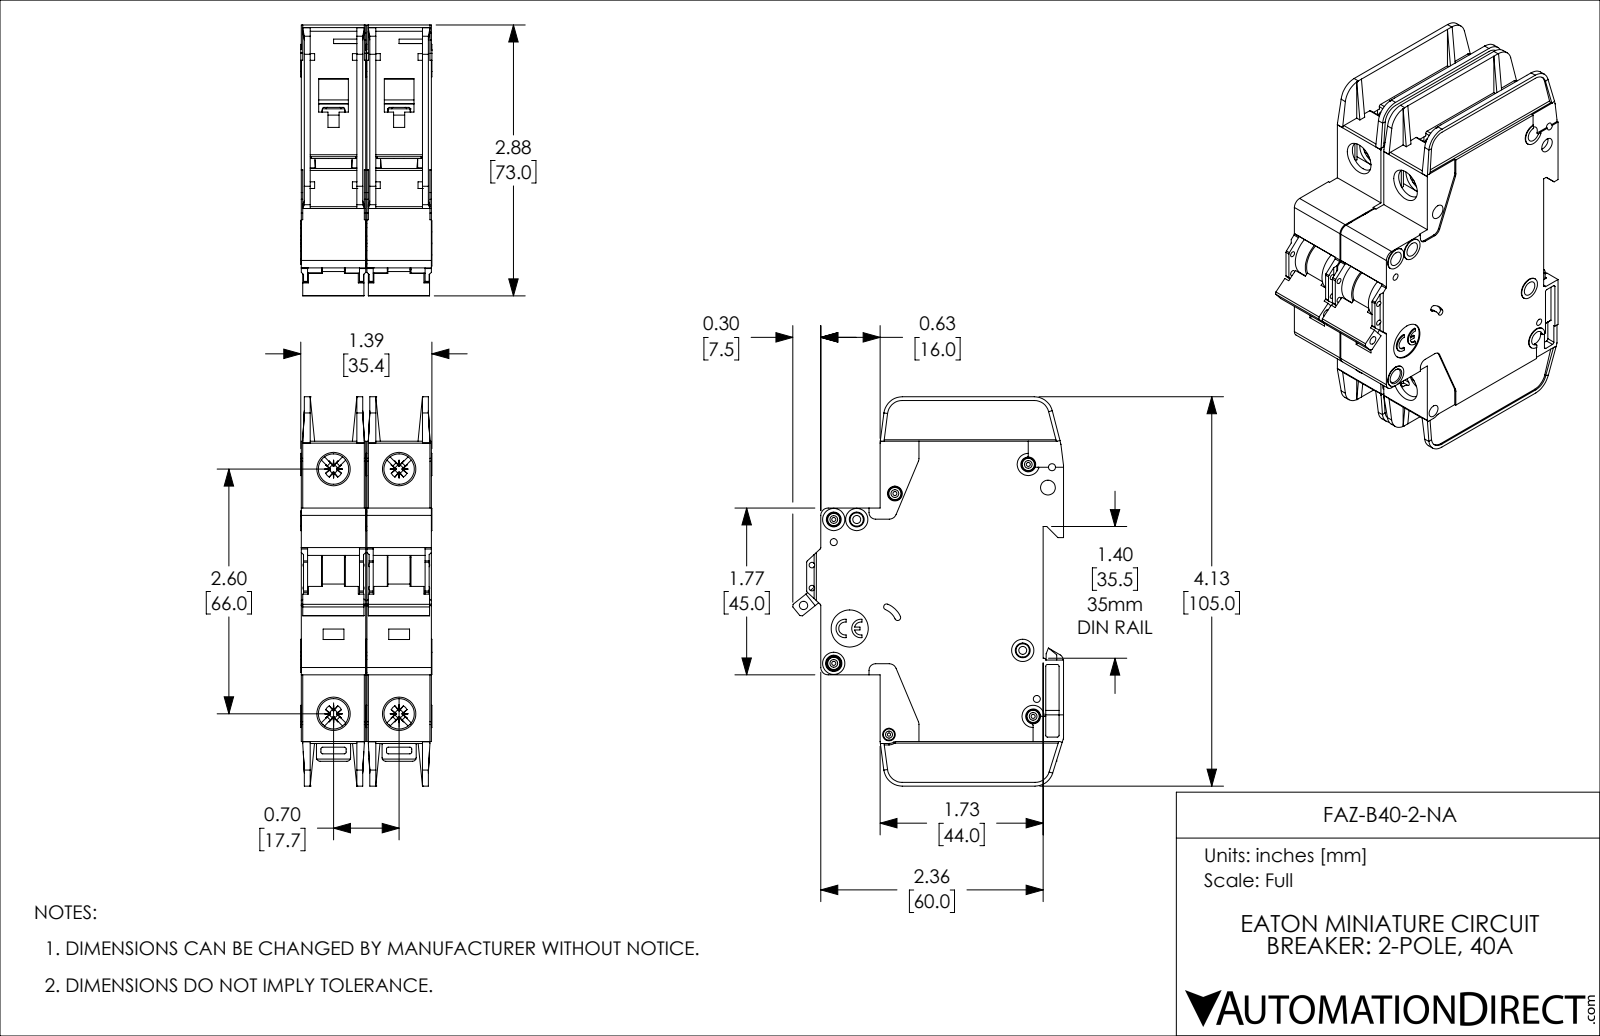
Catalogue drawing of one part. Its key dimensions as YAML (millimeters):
part_name: "FAZ-B40-2-NA"
step_written_by: "SolidWorks 2019 (AUTOMOTIVE_DESIGN)"
units: millimeters
bodies: {solids: 2, faces: 2254, planar: 1342, cylindrical: 714, other: 198}
overall_size: [105, 73.1, 35.4]
volume: 153500
surface_area: 52910
round_holes:
  - {diameter: 4, count: 8}
  - {diameter: 1.1, count: 5}
  - {diameter: 1.9, count: 4}
  - {diameter: 8.2, count: 4}
  - {diameter: 1.5, count: 2}
  - {diameter: 2.2, count: 2}
  - {diameter: 0.9, count: 1}
  - {diameter: 2.3, count: 1}
  - {diameter: 2.5, count: 1}
  - {diameter: 3.4, count: 1}
  - {diameter: 10, count: 1}
round_bosses_or_shafts:
  - {diameter: 3.3, count: 5}
  - {diameter: 6, count: 4}
  - {diameter: 3, count: 3}
  - {diameter: 2.5, count: 2}
partial_cylinders:
  - {radius: 0.5, count: 57}
  - {radius: 0.4, count: 20}
  - {radius: 1, count: 14}
  - {radius: 2, count: 10}
  - {radius: 1.1, count: 8}
  - {radius: 0.2, count: 5}
  - {radius: 5, count: 5}
  - {radius: 0.3, count: 4}
face_to_face_distances: [17.7, 1.2, 17.4, 15, 2.4, 16.2, 13.8, 35.1, 18.9, 16.5]
hole_center_spacings: [6.2, 13.6, 17.7, 22.1, 66, 68.3, 4.8, 5.1]
